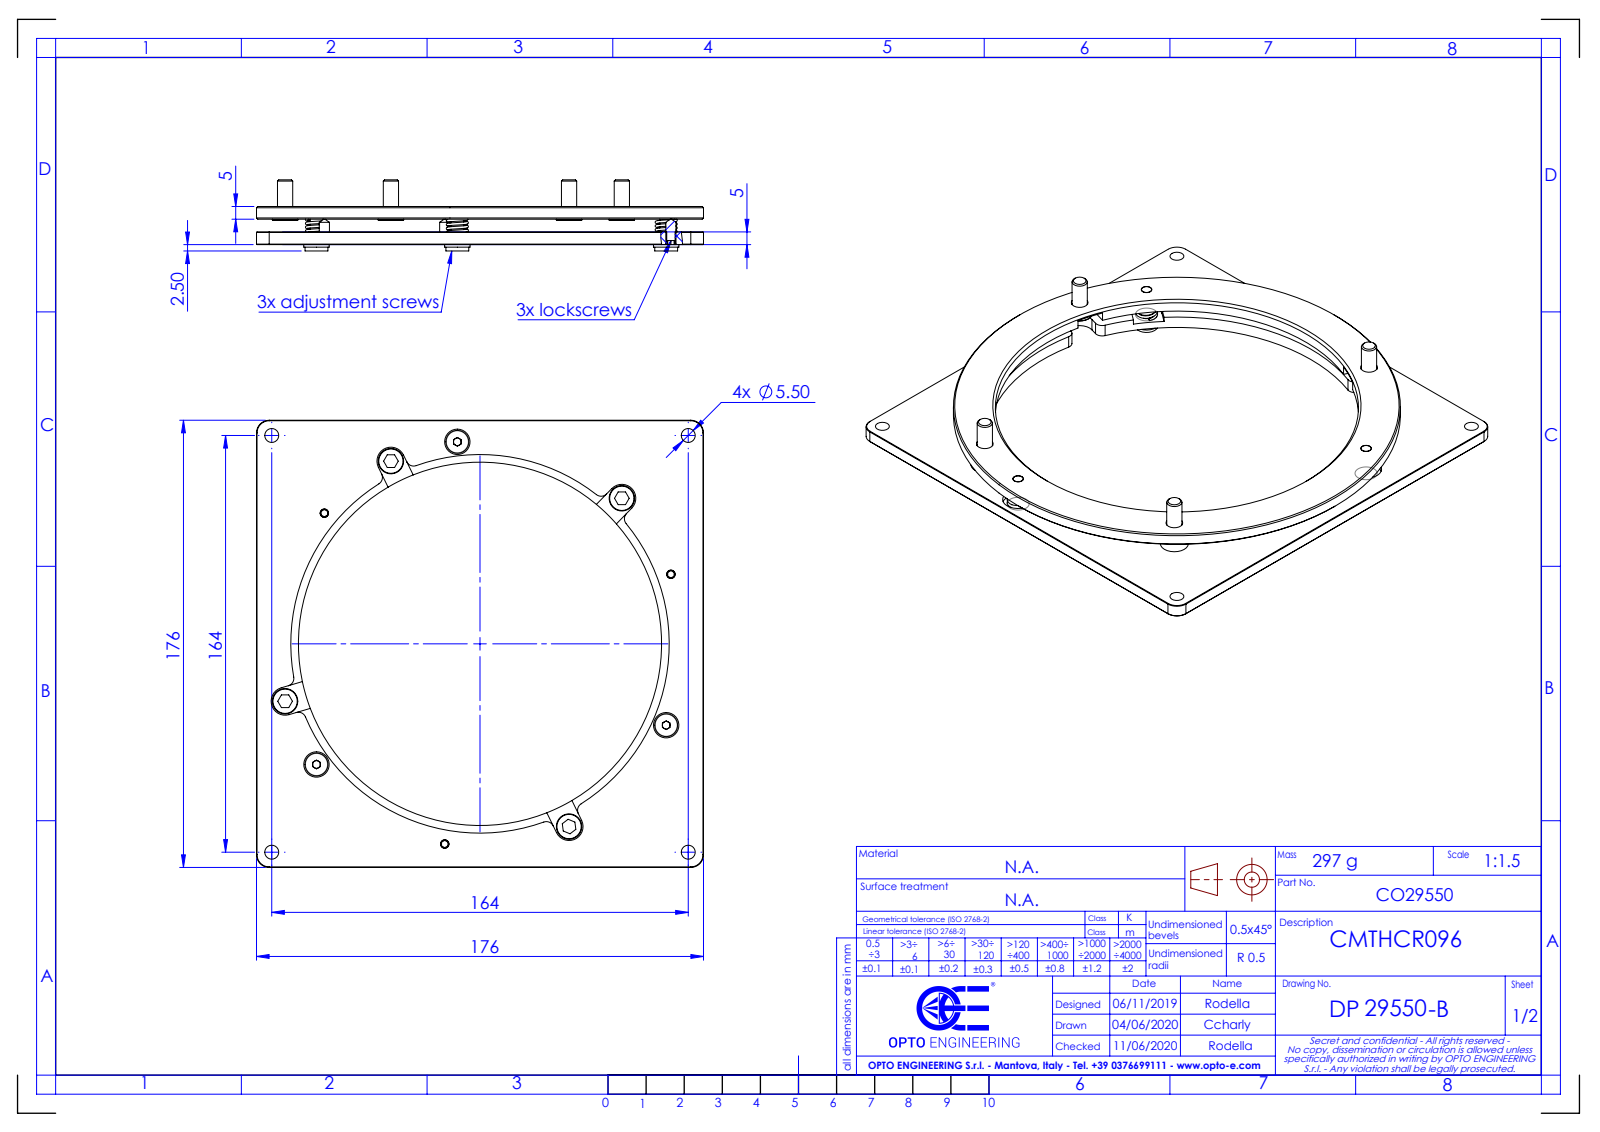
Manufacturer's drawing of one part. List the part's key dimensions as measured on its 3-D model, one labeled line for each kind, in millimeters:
Part name (STEP PRODUCT): DP29550
STEP written by: SolidWorks 2021 (CONFIG_CONTROL_DESIGN)
Units: millimetres
Bodies: 0 solids, 270 faces (118 planar, 102 cylindrical, 50 other)
Overall size (bounding box): 176 × 176 × 28
Round holes (diameter × count): ⌀5.5 ×4, ⌀6.6 ×4, ⌀4.2 ×2, ⌀5.8 ×1, ⌀143 ×1, ⌀149 ×1
Round bosses / shafts (diameter × count): ⌀10 ×7, ⌀6 ×4, ⌀9 ×3, ⌀5 ×3, ⌀4 ×3, ⌀176 ×1
Partial cylindrical surfaces — rounded edges, fillets, slot ends (radius × count): R3 ×8, R5 ×4, R5.5 ×4, R6.1 ×3
Main face-to-face distances: 5, 10, 15, 176, 1.5, 10.5, 12, 13.5, 8.5, 3.5
Hole centre spacings: 80, 115.97, 164, 48, 117.5, 160.9, 193.37, 231.93
